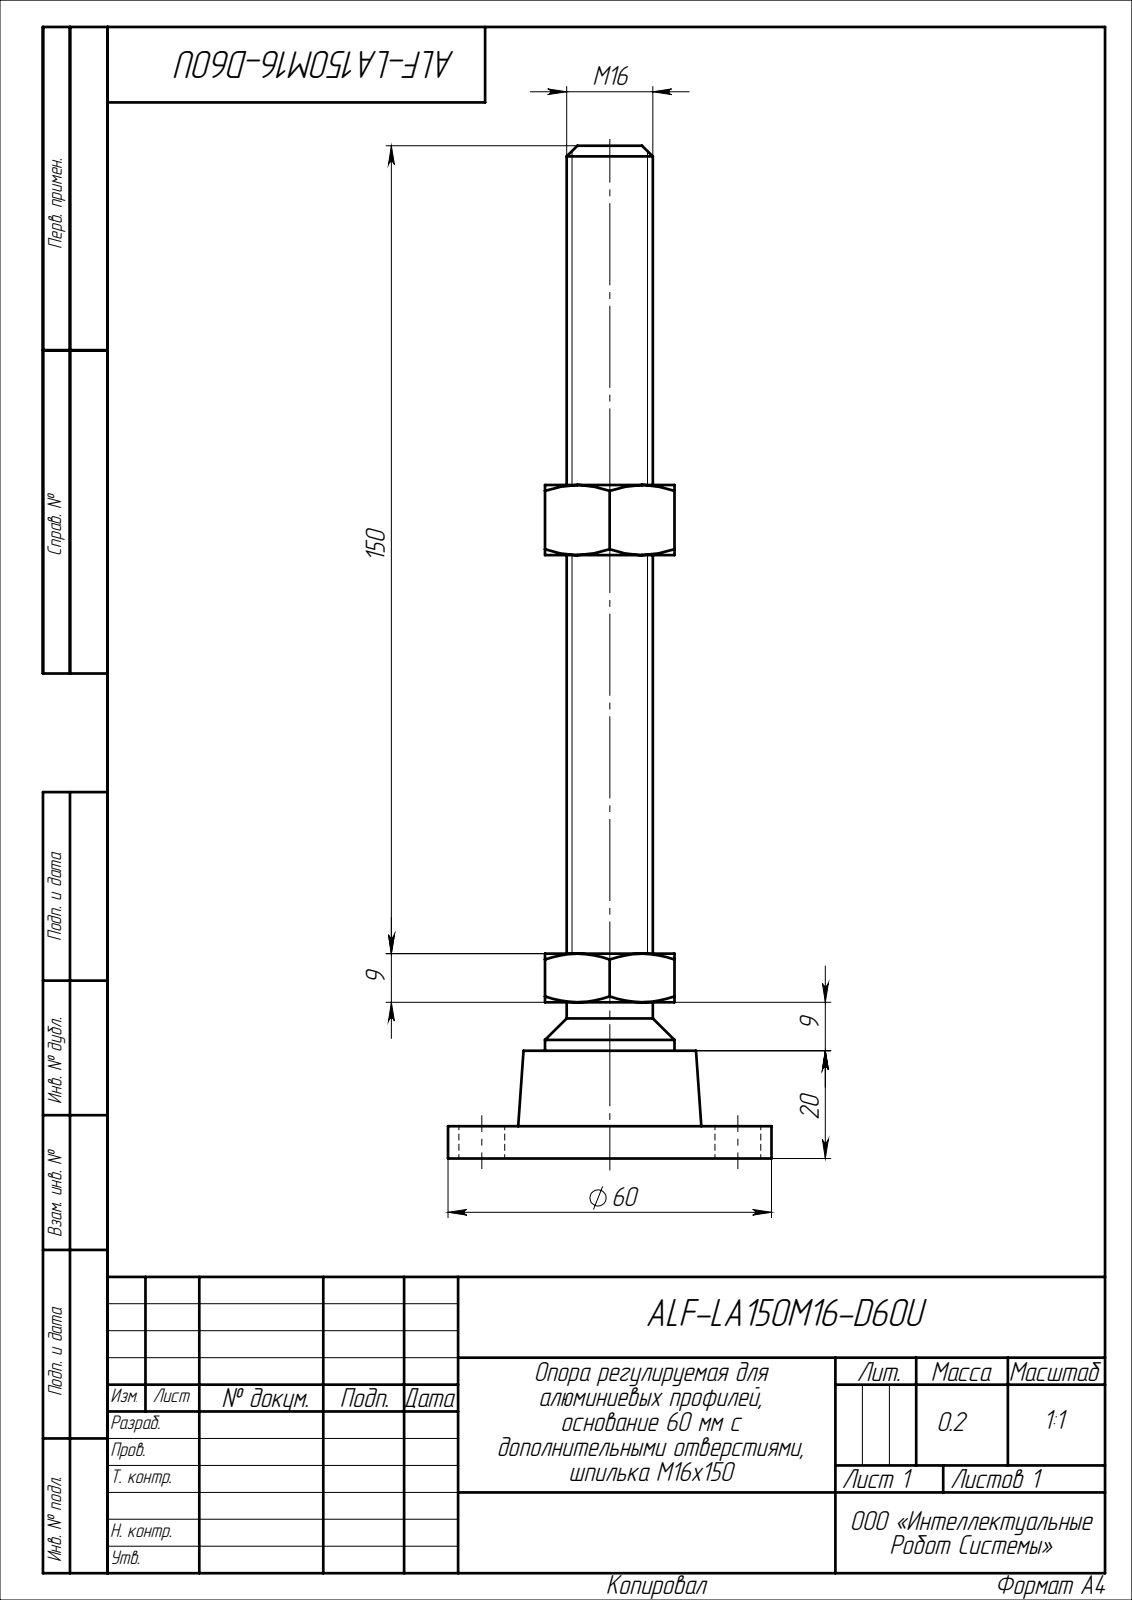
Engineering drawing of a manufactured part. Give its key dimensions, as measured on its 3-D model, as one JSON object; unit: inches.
{"part_name": "ALF-LA150M16-D60U", "step_written_by": "SolidWorks 2022 (CONFIG_CONTROL_DESIGN)", "units": "inches", "bodies": {"solids": 1, "faces": 64, "planar": 20, "cylindrical": 14, "other": 30}, "overall_size": [7.402, 2.362, 2.362], "volume_in3": 4.236, "surface_area_in2": 28.5, "round_holes": [[0.335, 2]], "round_bosses_or_shafts": [[2.362, 1], [0.945, 1], [0.63, 1]], "face_to_face_distances": [0.236, 0.945, 0.354, 0.787, 0.551, 1.142, 0.906, 1.496, 1.26, 0.709], "hole_center_spacings": [1.87]}
